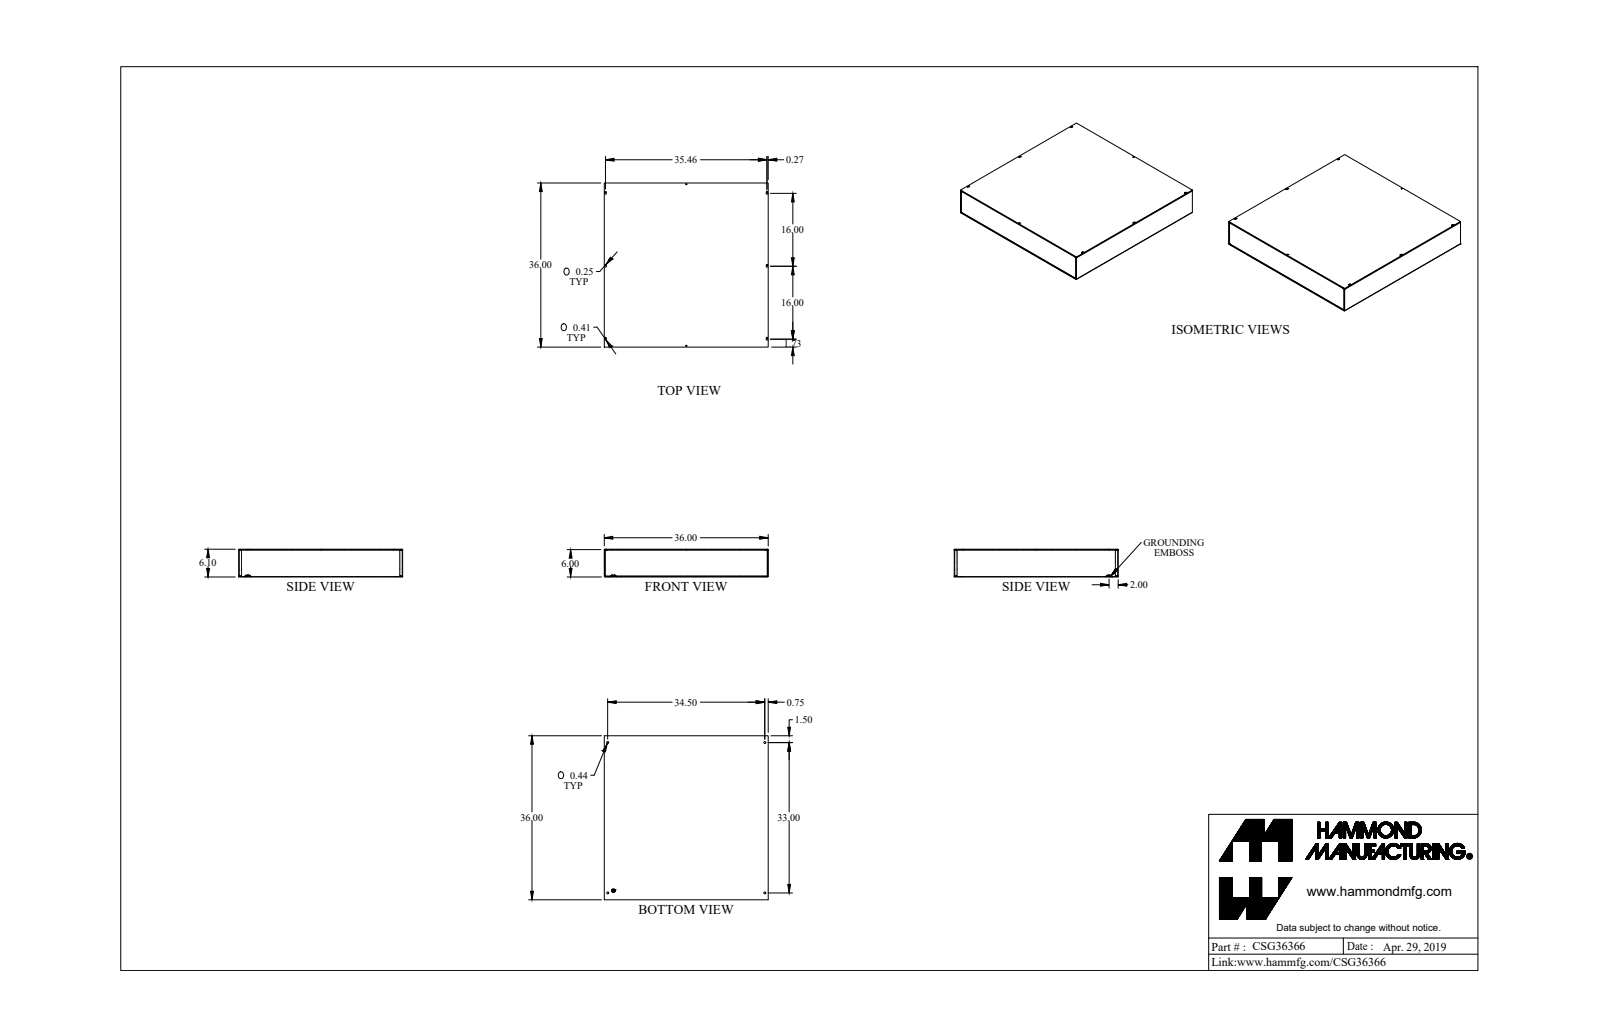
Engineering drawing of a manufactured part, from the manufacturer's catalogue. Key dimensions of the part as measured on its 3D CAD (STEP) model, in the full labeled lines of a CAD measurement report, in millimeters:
Part name (STEP PRODUCT): CSG36366_Default
STEP written by: SolidWorks 2019 (CONFIG_CONTROL_DESIGN)
Units: millimetres
Bodies: 4 solids, 221 faces (121 planar, 92 cylindrical, 8 other)
Overall size (bounding box): 914.4 × 914.4 × 154.8
Volume: 5 498 000 mm³ · Surface area: 4 588 000 mm²
Round holes (diameter × count): ⌀4.3 ×9, ⌀11.1 ×4, ⌀6.4 ×2, ⌀12.7 ×1
Round bosses / shafts (diameter × count): ⌀12.5 ×1, ⌀9.1 ×1
Partial cylindrical surfaces — rounded edges, fillets, slot ends (radius × count): R1.2 ×12, R3.6 ×12, R2.4 ×8, R3.2 ×6, R5.2 ×6
Main face-to-face distances: 2.4, 152.4, 150, 154.8, 912, 914.4, 909.6, 4.8, 147.6, 2.8
Hole centre spacings: 17.6, 406.4, 419.3, 439.3, 452.5, 636.9, 825.6, 888.6
